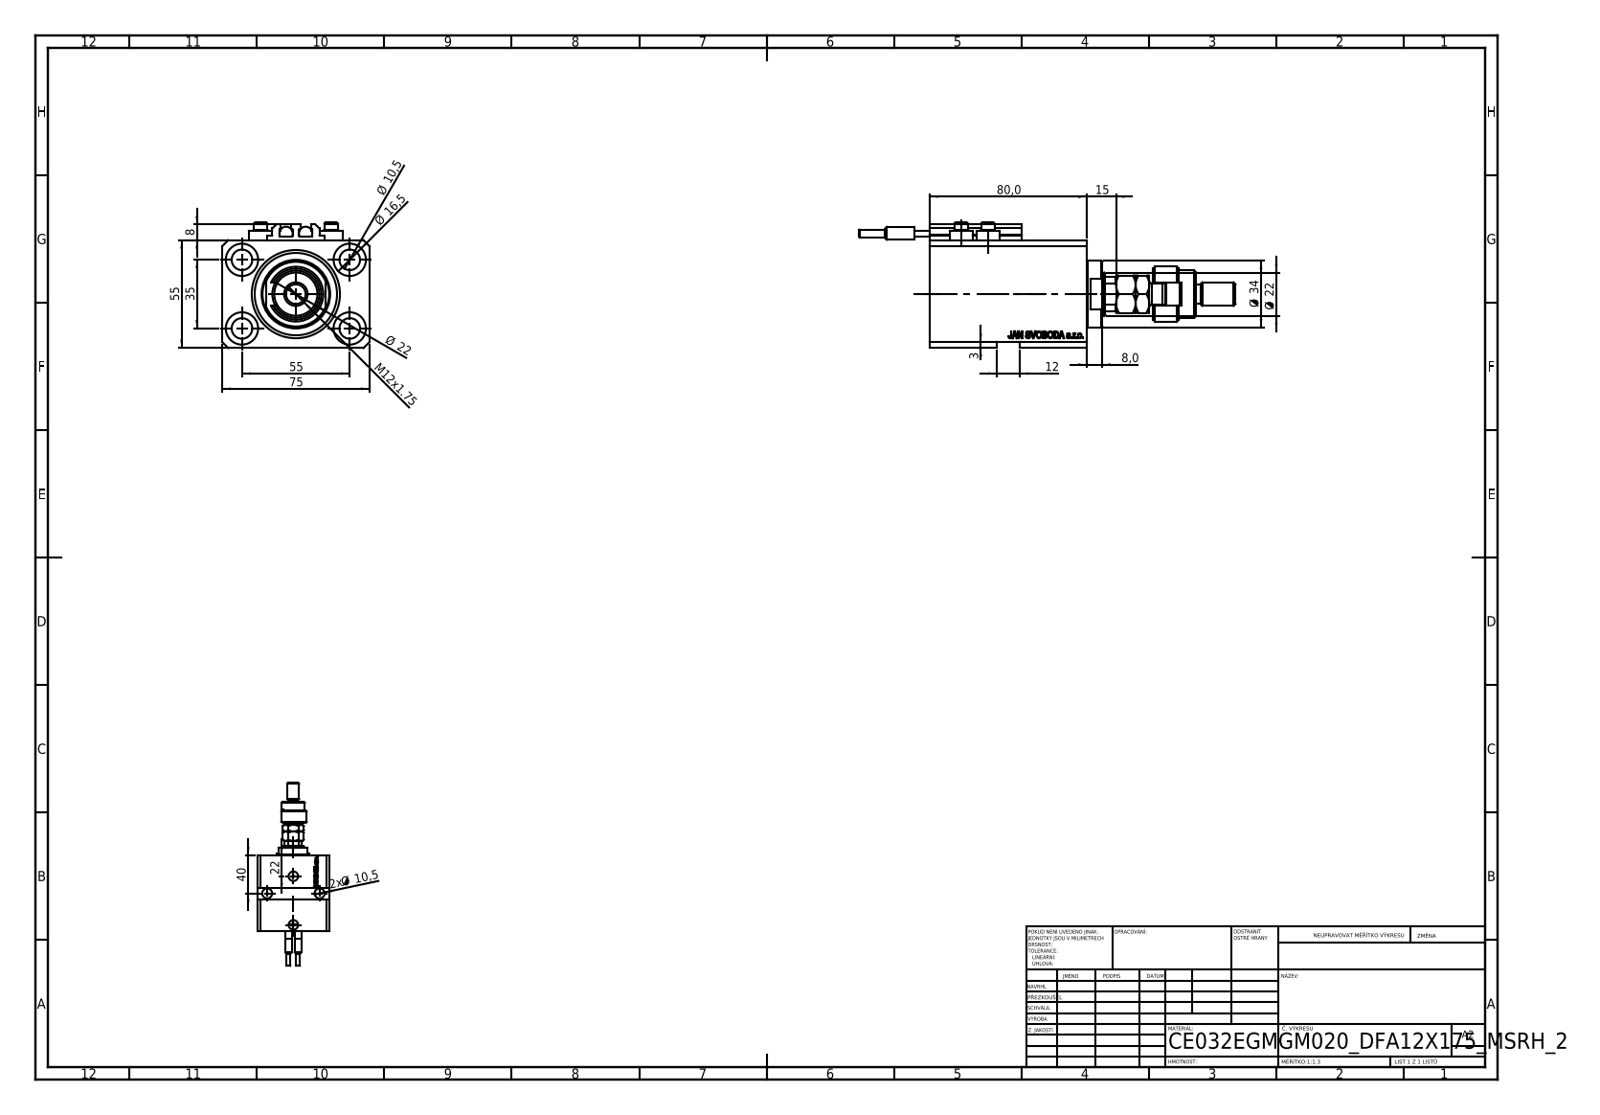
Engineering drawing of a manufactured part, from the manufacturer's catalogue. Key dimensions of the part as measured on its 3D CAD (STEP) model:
Part name (STEP PRODUCT): FEMALE_PART_FOR_DFA; V250CE_C_VCP; V250CE_VC_E; ALLEN BOLT V250CE (+3 more)
STEP written by: SolidWorks 2019 (CONFIG_CONTROL_DESIGN)
Units: millimetres
Bodies: 12 solids, 1201 faces (574 planar, 151 cylindrical, 476 other)
Overall size (bounding box): 192 × 75 × 64
Volume: 305 347 mm³ · Surface area: 84 335 mm²
Round holes (diameter × count): ⌀10.5 ×7, ⌀1.25 ×4, ⌀4 ×4, ⌀16.5 ×4, ⌀10 ×2, ⌀13.16 ×2, ⌀20 ×2, ⌀22 ×1, ⌀32 ×1, ⌀45 ×1
Round bosses / shafts (diameter × count): ⌀11.6 ×4, ⌀7 ×4, ⌀6.8 ×2, ⌀6.5 ×2, ⌀4 ×2, ⌀34 ×1, ⌀28 ×1, ⌀24 ×1
Partial cylindrical surfaces — rounded edges, fillets, slot ends (radius × count): R0.2 ×10, R9.75 ×1, R10.5 ×1
Main face-to-face distances: 55, 75, 15, 80, 3, 65, 55.1, 9.9, 57, 70.1
Hole centre spacings: 32.6, 55, 13.6, 14.09, 19.89, 20.12, 25.81, 28.48
